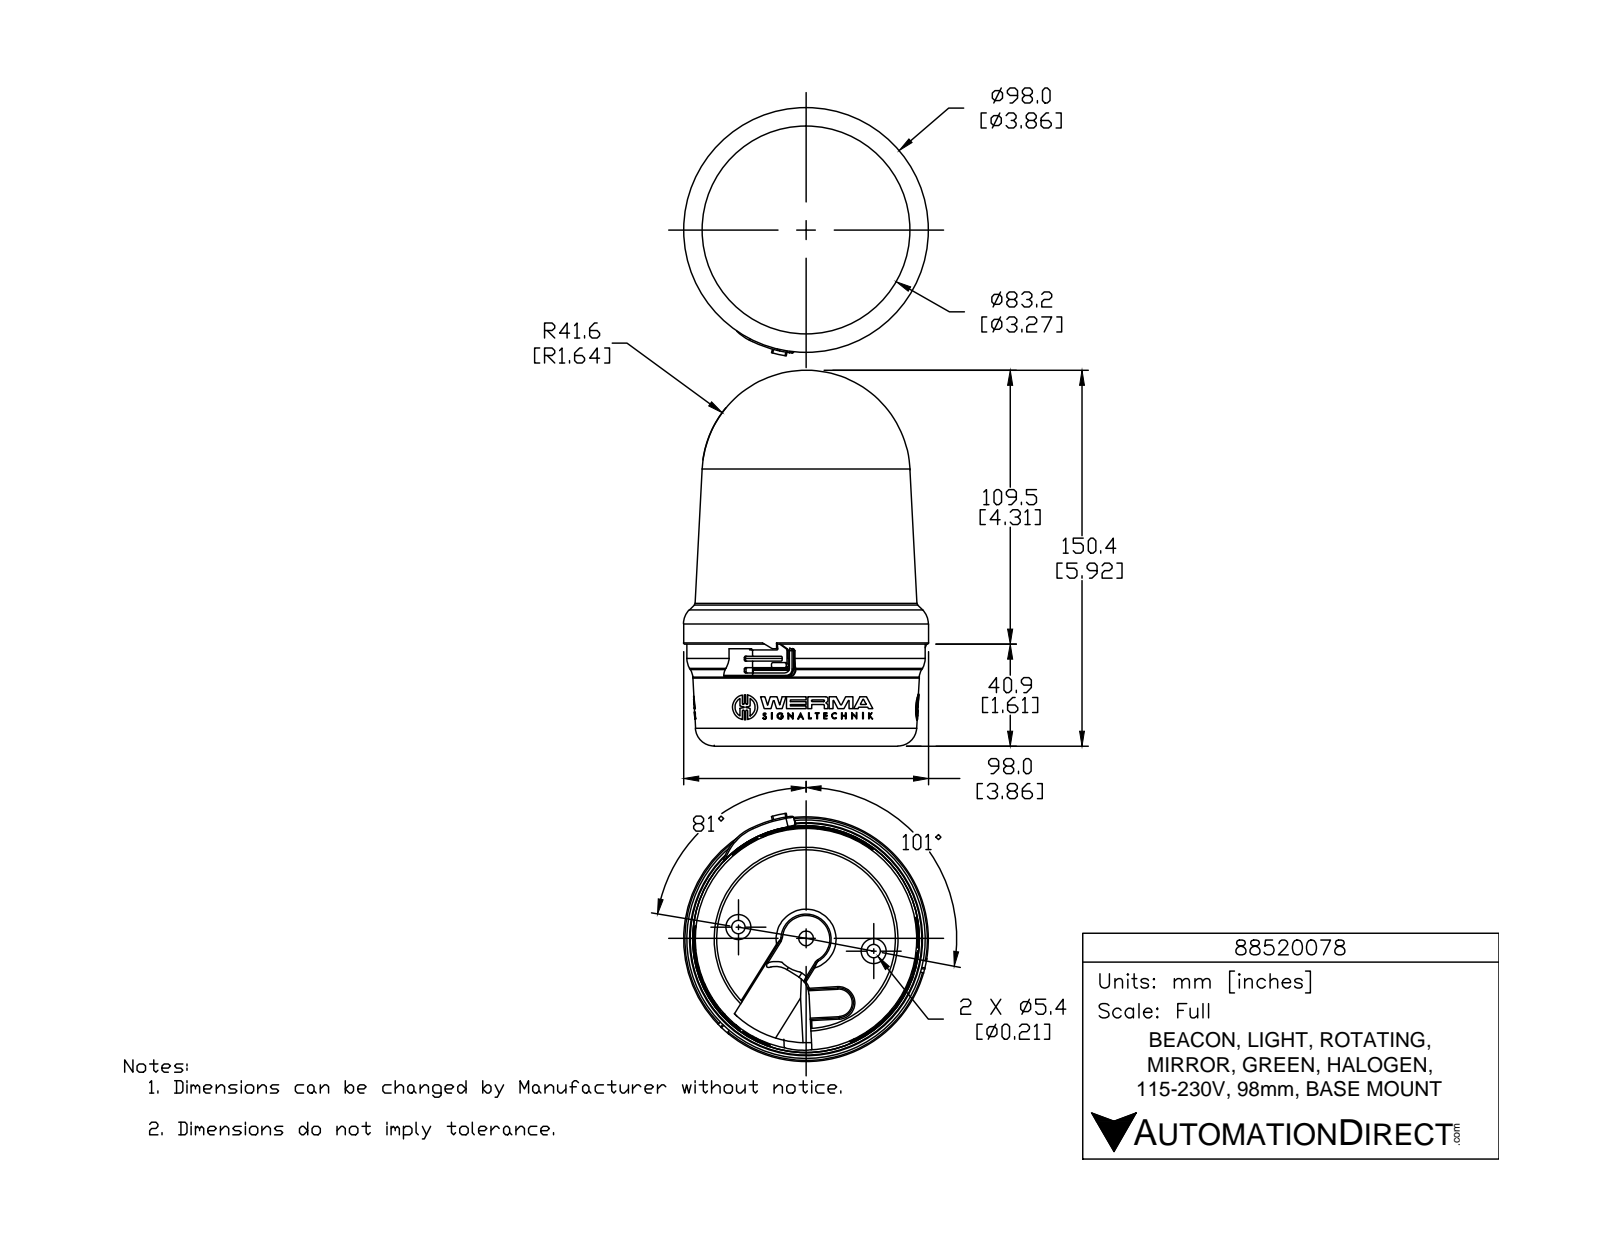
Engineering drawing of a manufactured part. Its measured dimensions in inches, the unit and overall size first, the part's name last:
Units: inches
Overall size (bounding box): 5.921 × 3.912 × 3.858
Round holes (diameter × count): ⌀0.068 ×3, ⌀0.213 ×2, ⌀0.409 ×2, ⌀2.815 ×1
Round bosses / shafts (diameter × count): ⌀0.395 ×3, ⌀0.099 ×3, ⌀0.394 ×2, ⌀3.858 ×1, ⌀3.756 ×1, ⌀3.571 ×1
Partial cylindrical surfaces — rounded edges, fillets, slot ends (radius × count): R0.02 ×21, R0.006 ×9, R0.006 ×6, R0.014 ×6, R0.014 ×6, R0.014 ×6, R0.229 ×6, R0.079 ×4
Main face-to-face distances: 0.059, 0.033, 0.27, 0.02, 0.289, 0.734, 0.768, 0.315, 1.319, 1.26
Hole centre spacings: 1.083, 2.165
Volume: 49.51 in³ · Surface area: 82.1 in²
Bodies: 1 solid, 969 faces (586 planar, 238 cylindrical, 145 other)
Part name (STEP PRODUCT): 88520078
STEP written by: SolidWorks 2015 (AUTOMOTIVE_DESIGN)
